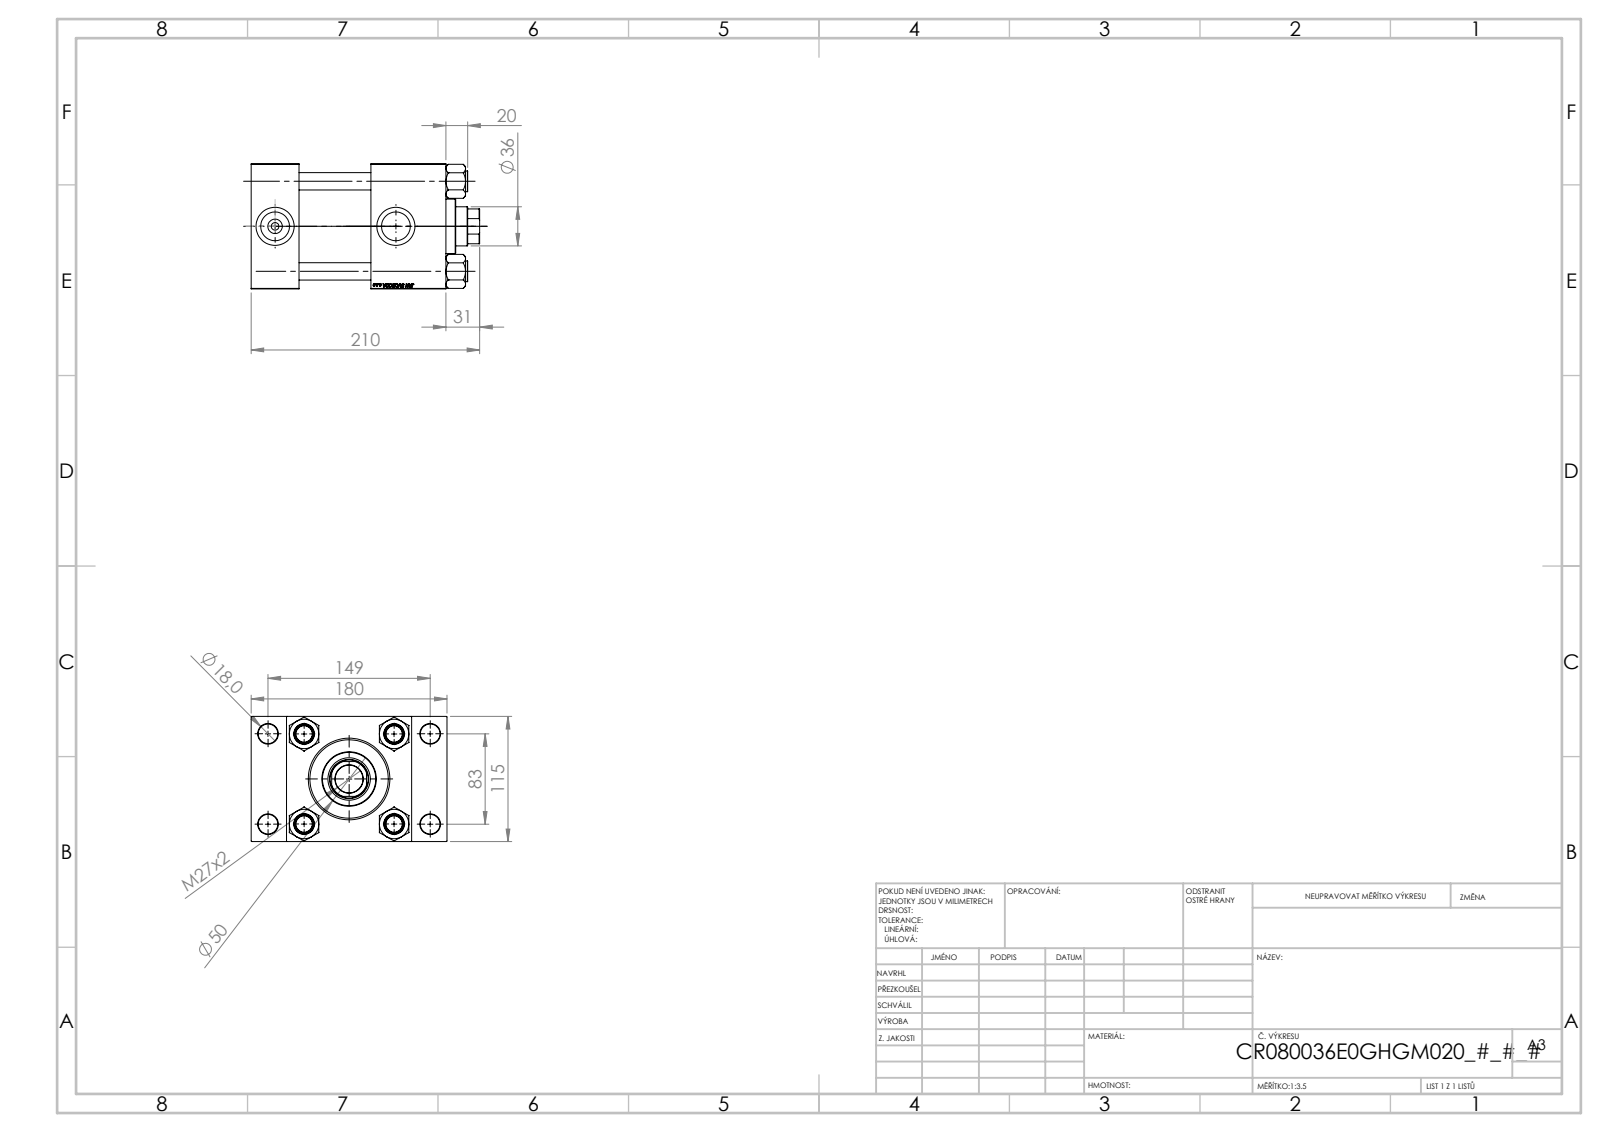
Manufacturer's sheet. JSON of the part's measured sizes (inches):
{"part_name": "V215CR_TYCINKA_E; V215CR_VCP_E; V215CR_E_Body; NUT_M5_E (+1 more)", "step_written_by": "SolidWorks 2019 (CONFIG_CONTROL_DESIGN)", "units": "inches", "bodies": {"solids": 11, "faces": 1190, "planar": 548, "cylindrical": 90, "other": 552}, "overall_size": [8.268, 7.087, 4.528], "volume_in3": 127.2, "surface_area_in2": 481, "round_holes": [[0.63, 4], [0.709, 4], [0.098, 2], [0.276, 2], [1.041, 2], [1.378, 2], [1.004, 1], [1.417, 1], [1.535, 1], [2.402, 1], [2.835, 1], [3.15, 1]], "round_bosses_or_shafts": [[0.748, 4], [3.386, 1], [1.969, 1]], "partial_cylinders_radius": [[0.689, 1]], "face_to_face_distances": [4.528, 1.732, 7.047, 5.315, 1.28, 5.807, 4.331, 2.598, 2.717, 0.787], "hole_center_spacings": [1.305, 1.652, 2.276, 2.302, 3.256, 3.357, 3.393, 3.513]}
